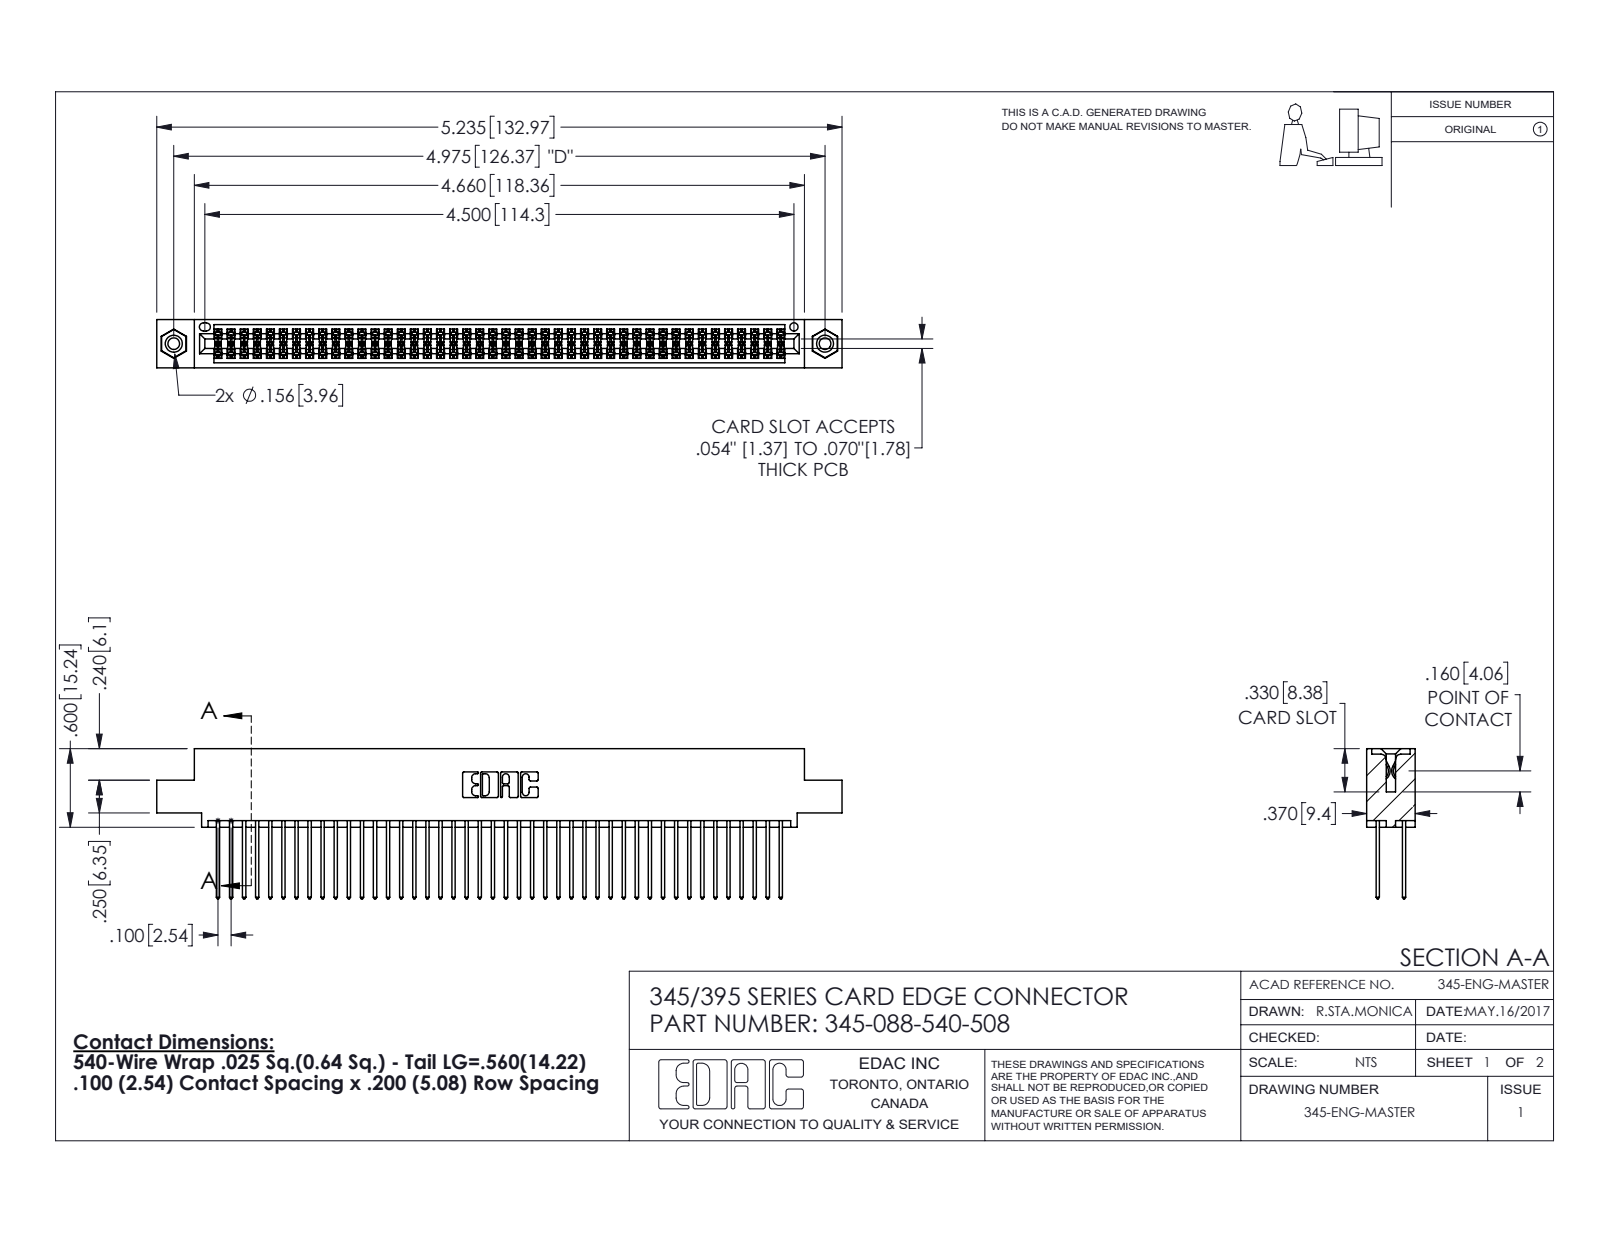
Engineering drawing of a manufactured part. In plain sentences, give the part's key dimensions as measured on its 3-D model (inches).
The part is named "345-088-540-508; 345-250-001_345-250-003-102; 345 Part_0.110 Offset - 0.156 Dia-TI; 345-292-001_345-293-140". Its 3-D file was written by "SolidWorks 2016 (CONFIG_CONTROL_DESIGN)". It is 91 solids with 4590 faces: 3020 planar, 1554 cylindrical and 16 other. Overall it measures 5.235 by 1.147 by 0.37 inches. Its volume is 0.805 cubic inches and its surface area 32.84 square inches. Round holes: 2 of diameter 0.089, 2 of diameter 0.125, 2 of diameter 0.156, 1 of diameter 0.064. Round bosses or shafts: 2 of diameter 0.155. Partial cylindrical surfaces (rounded edges, fillets, slot ends): 132 of radius 0.006, 88 of radius 0.01, 22 of radius 0.01, 6 of radius 0.007, 6 of radius 0.031, 3 of radius 0.026, 2 of radius 0.014, 2 of radius 0.019. The main face-to-face distances are 0.072, 0.298, 0.2, 0.098, 0.272, 0.025, 0.37, 0.225, 0.175, 0.149. The hole center spacings are 0.27, 4.739, 4.975.
